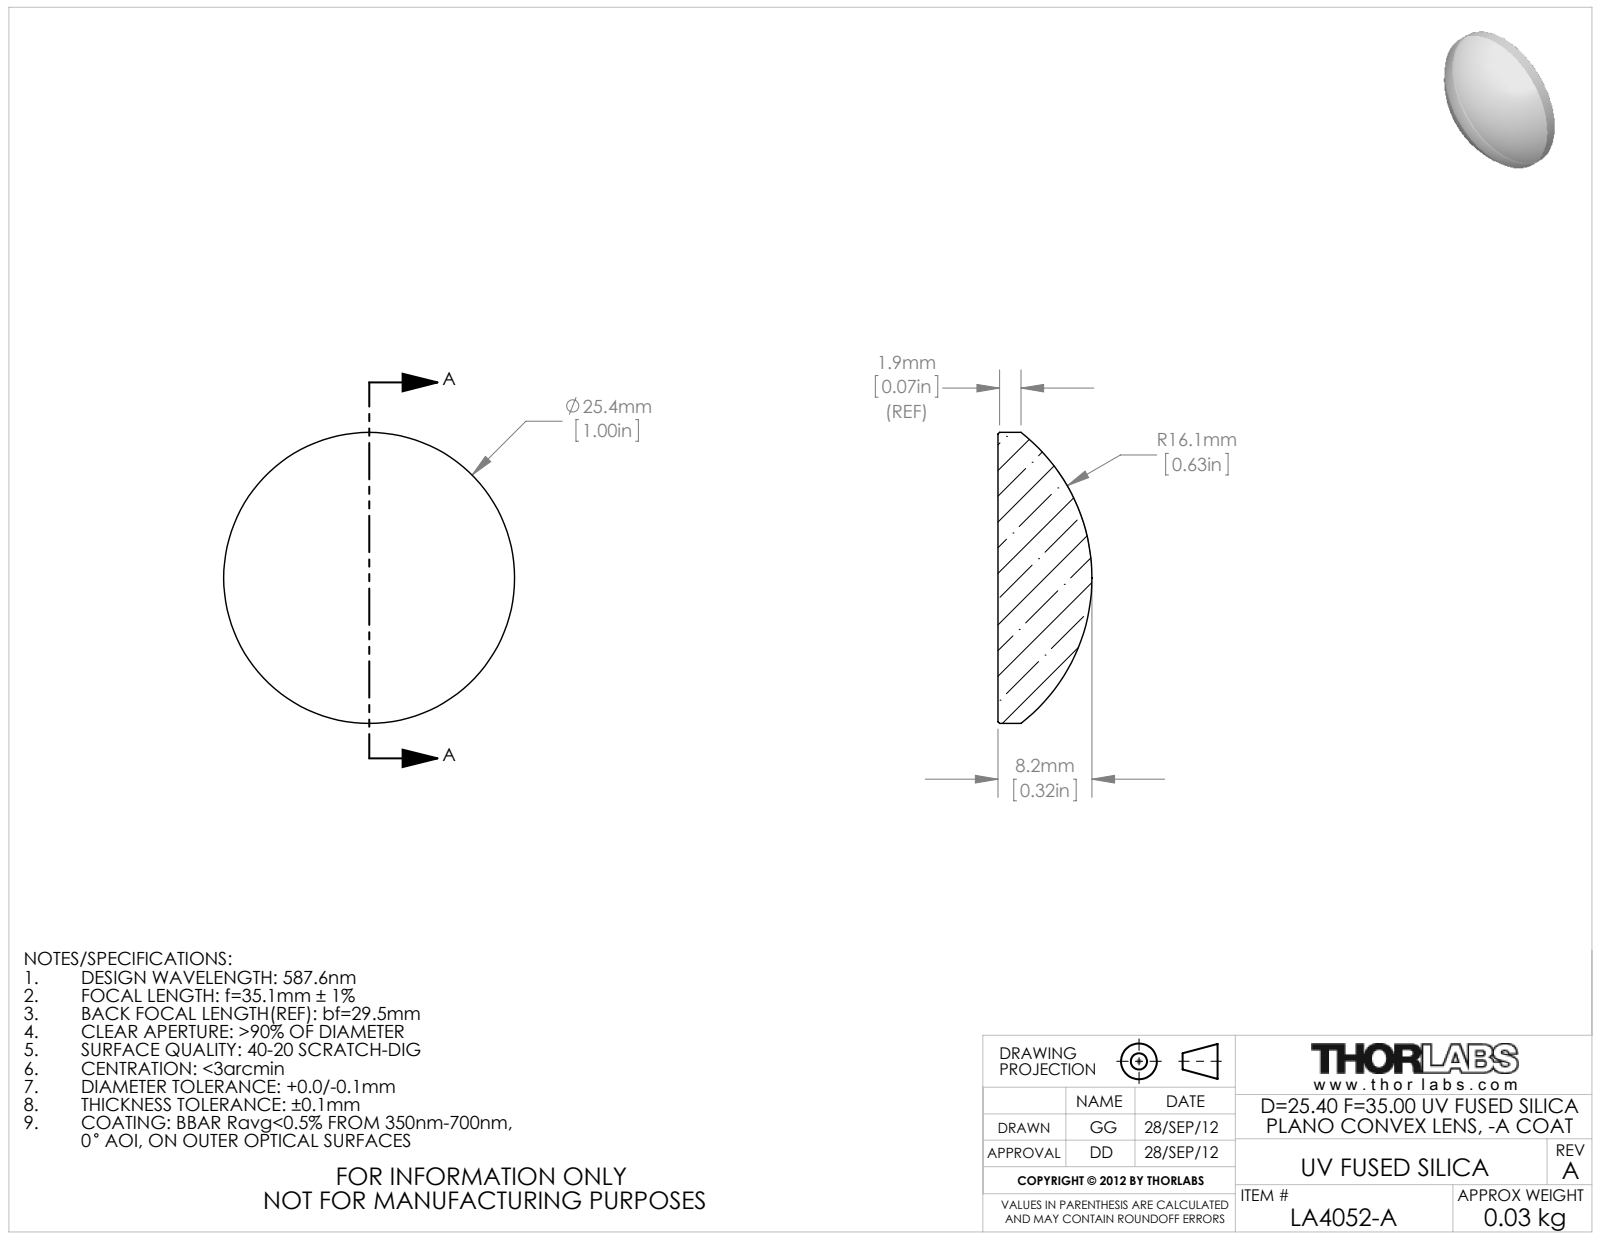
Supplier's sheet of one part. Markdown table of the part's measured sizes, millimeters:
| quantity | value |
| --- | --- |
| part name | 24978-E0W |
| STEP written by | SolidWorks 2011 (CONFIG_CONTROL_DESIGN) |
| units | millimeters |
| bodies | 1 solid, 7 faces (1 planar, 2 cylindrical, 4 other) |
| overall size | 25.4 × 25.4 × 8.2 |
| volume | 2 709 mm³ |
| surface area | 1 287 mm² |
| round bosses / shafts (diameter × count) | 25.4 × 1 |
